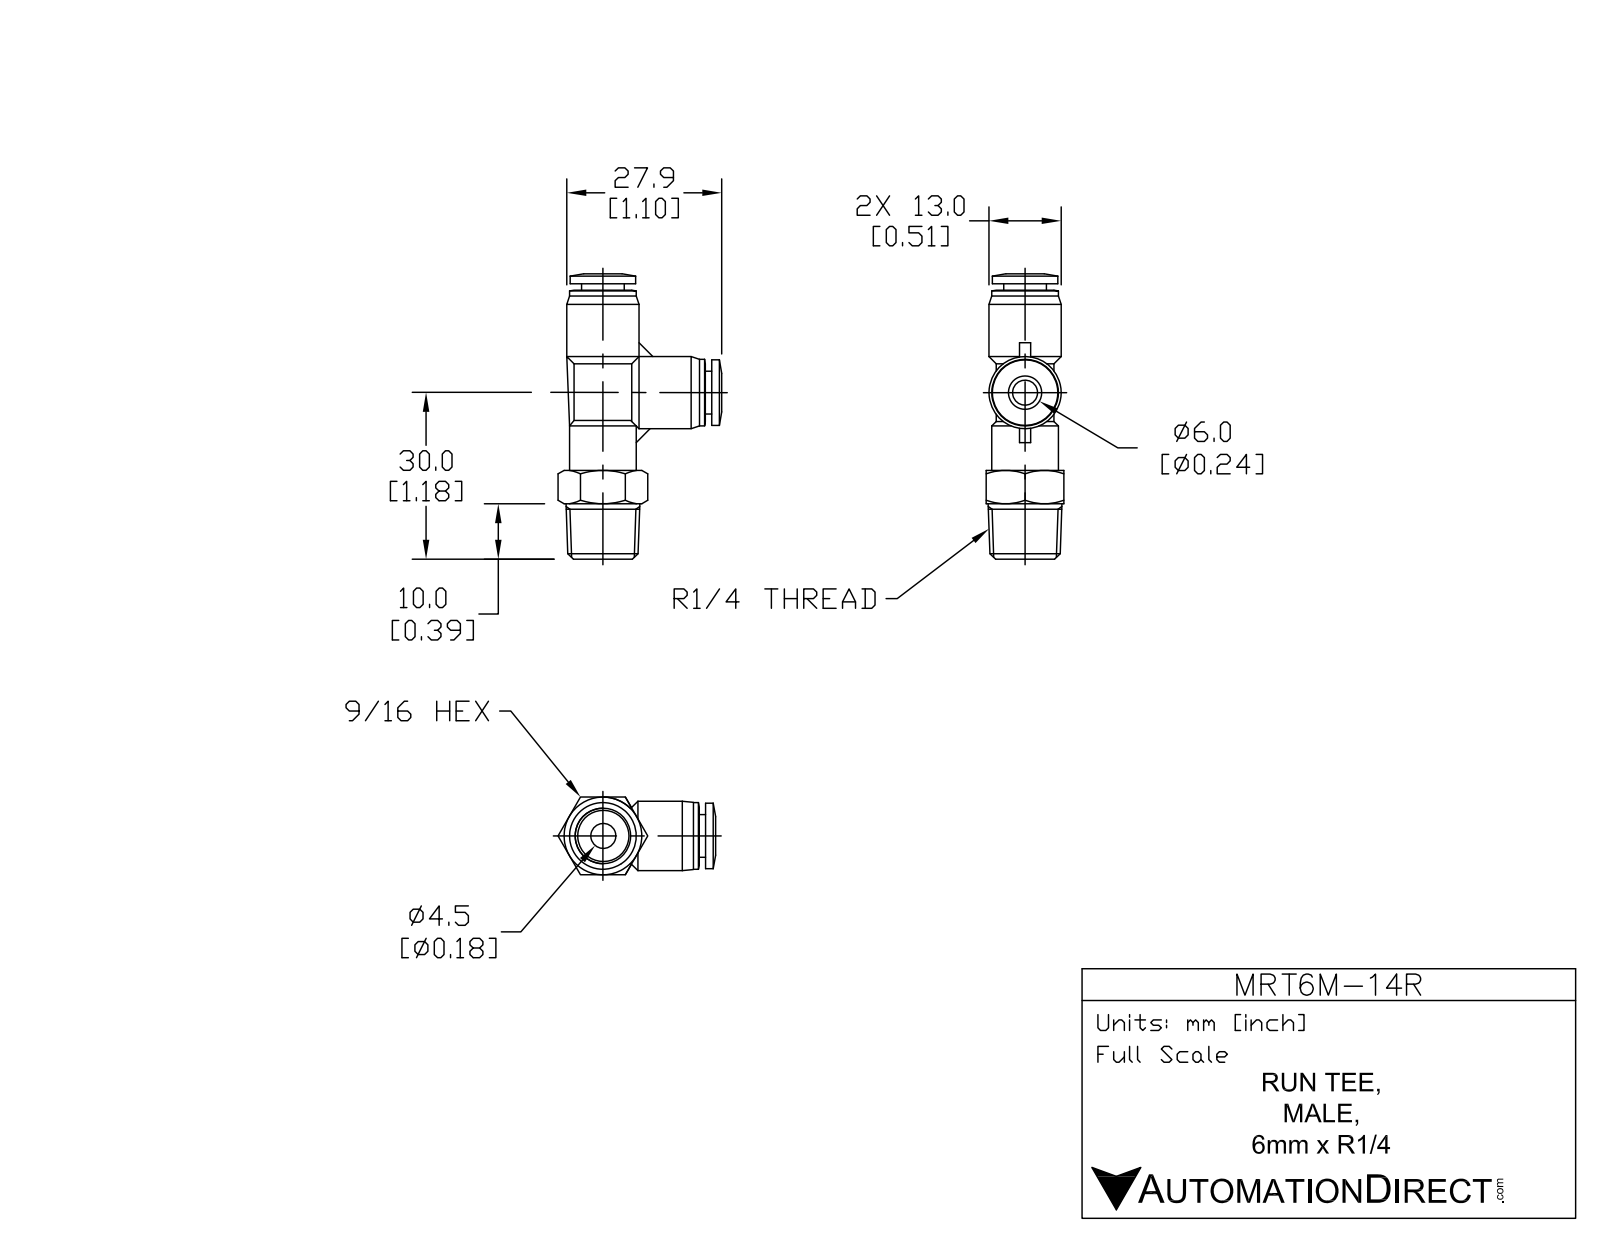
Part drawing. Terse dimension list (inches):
name: MRT6M-14R
written by: SolidWorks 2015 (AUTOMOTIVE_DESIGN)
unit: in
bodies: 1 solid, 98 faces (25 planar, 30 cylindrical, 43 other)
size: 2.024 × 1.161 × 0.551
volume: 0.405 in³; area: 6.723 in²
holes: 2× ⌀0.157, 2× ⌀0.248
bosses: 2× ⌀0.512, 2× ⌀0.472, 2× ⌀0.465, 2× ⌀0.409, 2× ⌀0.303
face distances: 0.551, 0.045, 1.953, 0.236, 0.63, 1.323, 0.315, 1.907, 1.278, 0.53
